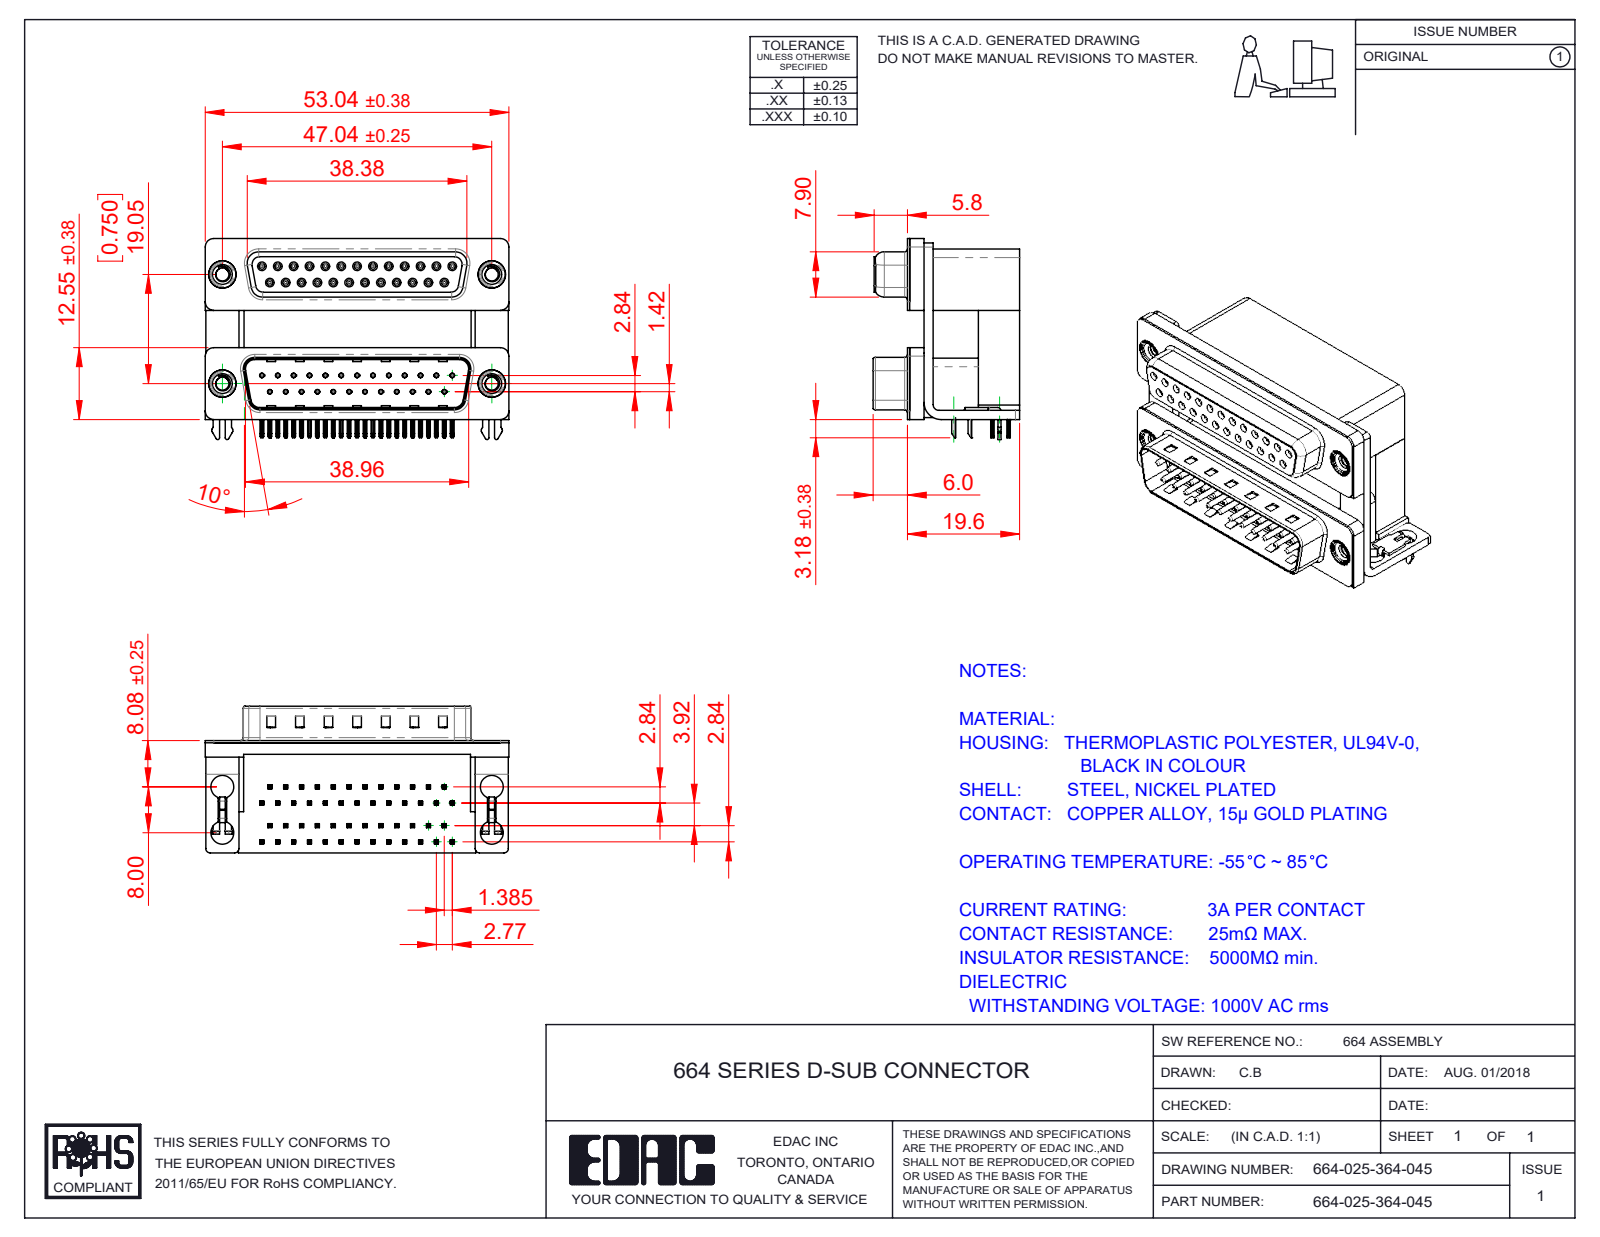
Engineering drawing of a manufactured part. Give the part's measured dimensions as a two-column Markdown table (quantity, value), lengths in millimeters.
| quantity | value |
| --- | --- |
| part name | 664 Contact Top Lower; 664 Threaded Rivet_4-40; 664 Housing Upper_25 Contacts M; 664 Mounting Bracket_2ProngM (+8 more) |
| STEP written by | SolidWorks 2020 (CONFIG_CONTROL_DESIGN) |
| units | millimeters |
| bodies | 63 solids, 6311 faces (3335 planar, 1573 cylindrical, 1403 other) |
| overall size | 53.04 × 35.1 × 25.6 |
| volume | 22 484 mm³ |
| surface area | 24 222 mm² |
| round holes (diameter × count) | 0.8 × 50, 0.35 × 25, 0.9 × 25, 4 × 8, 2.26 × 4, 3.5 × 4, 4.8 × 4, 5 × 4 |
| round bosses / shafts (diameter × count) | 1.2 × 25, 0.75 × 25, 4.9 × 4, 4.75 × 4, 3.9 × 4 |
| partial cylindrical surfaces (radius × count) | 0.1 × 201, 0.25 × 106, 0.15 × 100, 0.12 × 50, 0.35 × 50, 0.34 × 25, 0.5 × 16, 1.5 × 14 |
| main face-to-face distances | 0.4, 19.2, 7.2, 12, 10.69, 16.7, 9.5, 2.5, 2.84, 18.71 |
| hole center spacings | 2.77, 3.16, 5.54, 8.31, 11.08, 13.85, 16.62, 5.03 |
